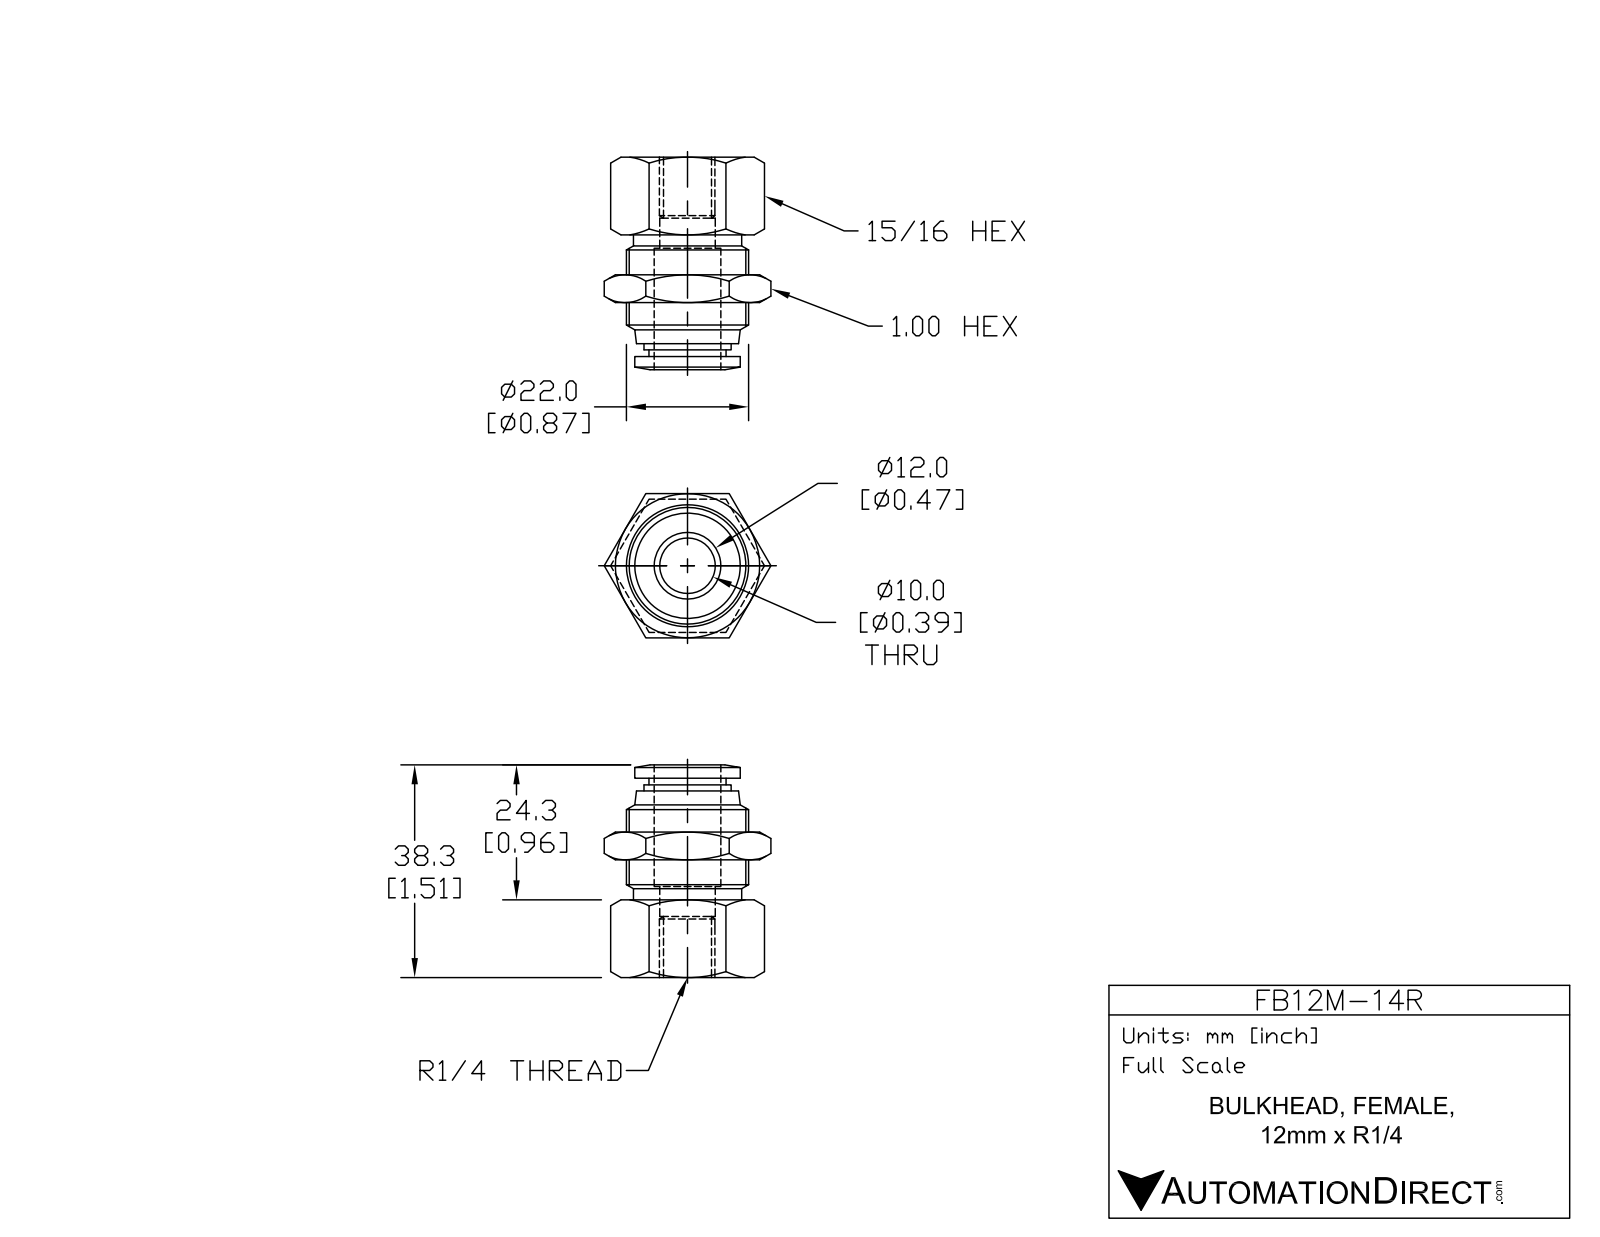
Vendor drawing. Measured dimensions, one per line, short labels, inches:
name: FB12M-14R
written by: SolidWorks 2015 (AUTOMOTIVE_DESIGN)
unit: in
bodies: 1 solid, 78 faces (22 planar, 16 cylindrical, 40 other)
size: 1.508 × 1.182 × 1.024
volume: 0.701 in³; area: 8.871 in²
holes: 1× ⌀0.394, 1× ⌀0.484
bosses: 1× ⌀0.866, 1× ⌀0.768, 1× ⌀0.748, 1× ⌀0.618, 1× ⌀0.547
face distances: 0.945, 0.039, 0.984, 1.024, 0.551, 0.834, 0.283, 1.031, 0.48, 0.197
